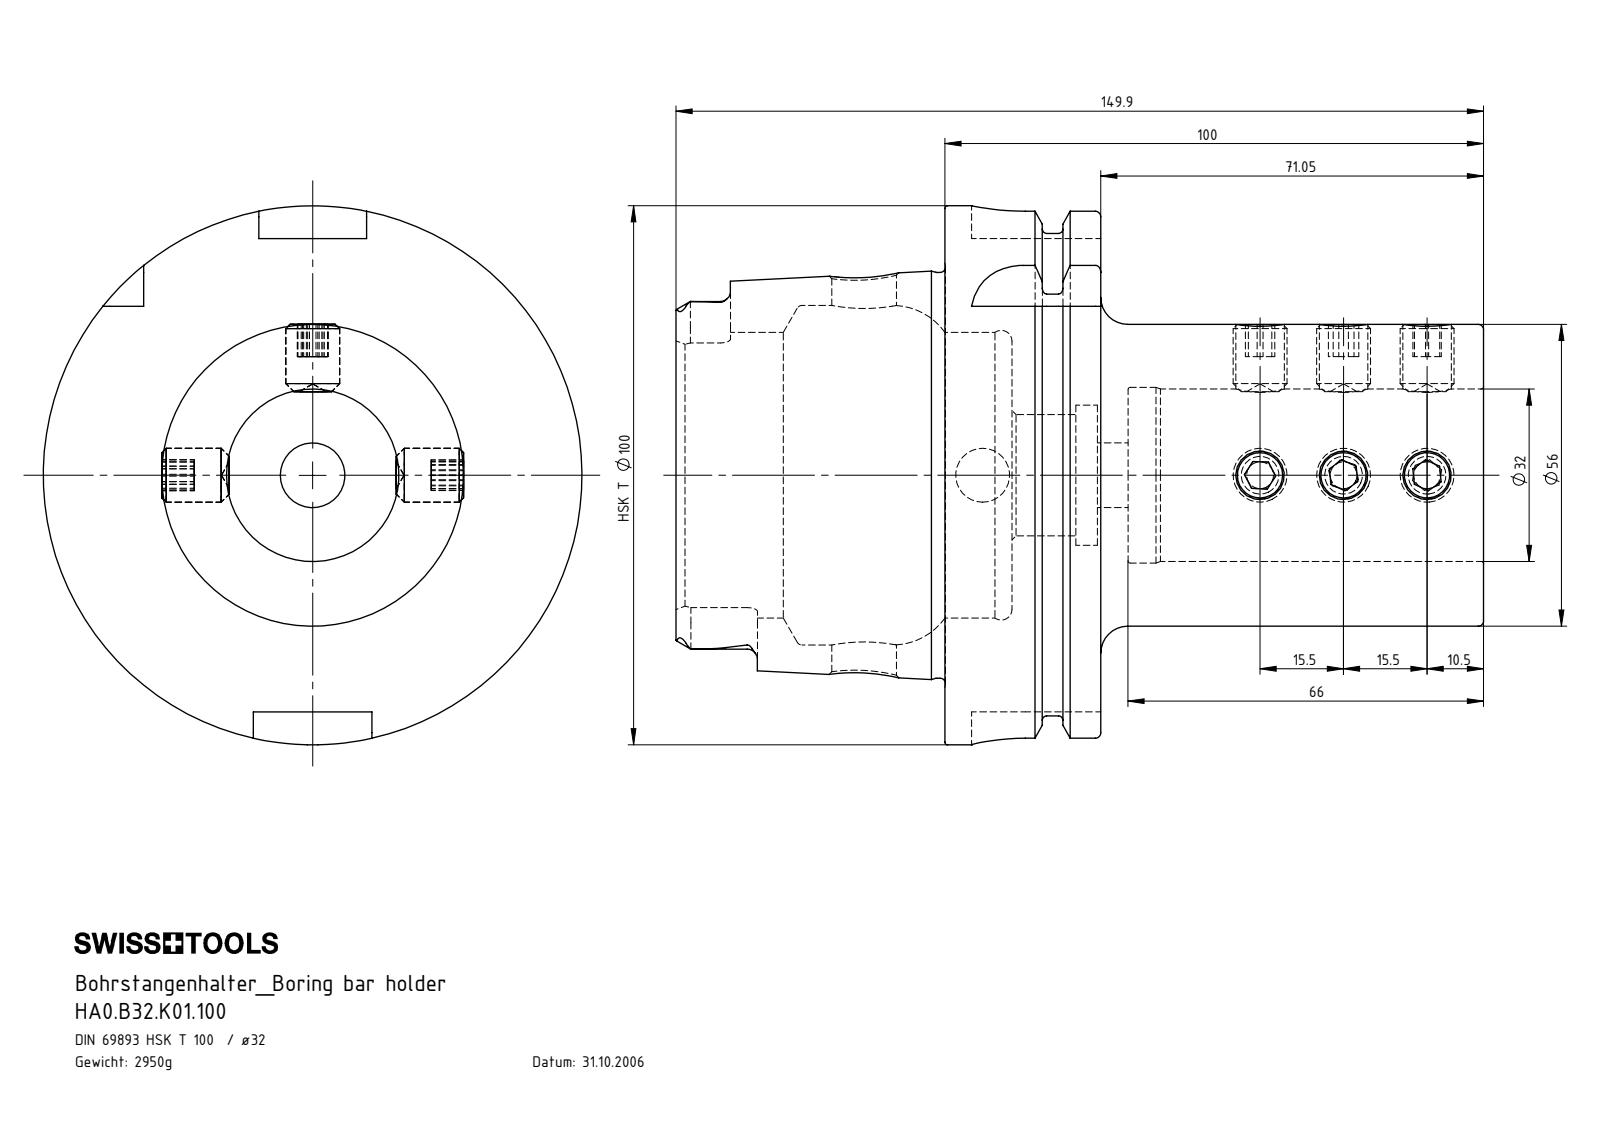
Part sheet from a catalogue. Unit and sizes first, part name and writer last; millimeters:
Units: millimetres
Overall size (bounding box): 149.9 × 100 × 100
Round holes (diameter × count): ⌀9 ×6, ⌀12 ×2, ⌀10 ×1, ⌀22.5 ×1, ⌀26 ×1, ⌀32 ×1, ⌀32.6 ×1, ⌀53 ×1, ⌀63 ×1
Round bosses / shafts (diameter × count): ⌀10 ×6, ⌀100 ×1, ⌀91.95 ×1, ⌀75.26 ×1, ⌀56 ×1
Partial cylindrical surfaces — rounded edges, fillets, slot ends (radius × count): R1.9 ×6, R4.88 ×4, R10 ×4
Main face-to-face distances: 28.95, 12.45, 16.5, 100, 87.55, 71.05, 49.9, 62.35, 78.85, 149.9
Hole centre spacings: 15.5, 31, 51.5, 67, 73.5, 82.5, 89, 104.5
Volume: 375 812 mm³ · Surface area: 75 738 mm²
Bodies: 10 solids, 331 faces (122 planar, 86 cylindrical, 123 other)
Part name (STEP PRODUCT): HA0.B32.K01.100; W10-ER1.001.012; HA0-B32.K01.100_B_Fertigbearbeitung
STEP written by: SolidWorks 2012 (AUTOMOTIVE_DESIGN)
